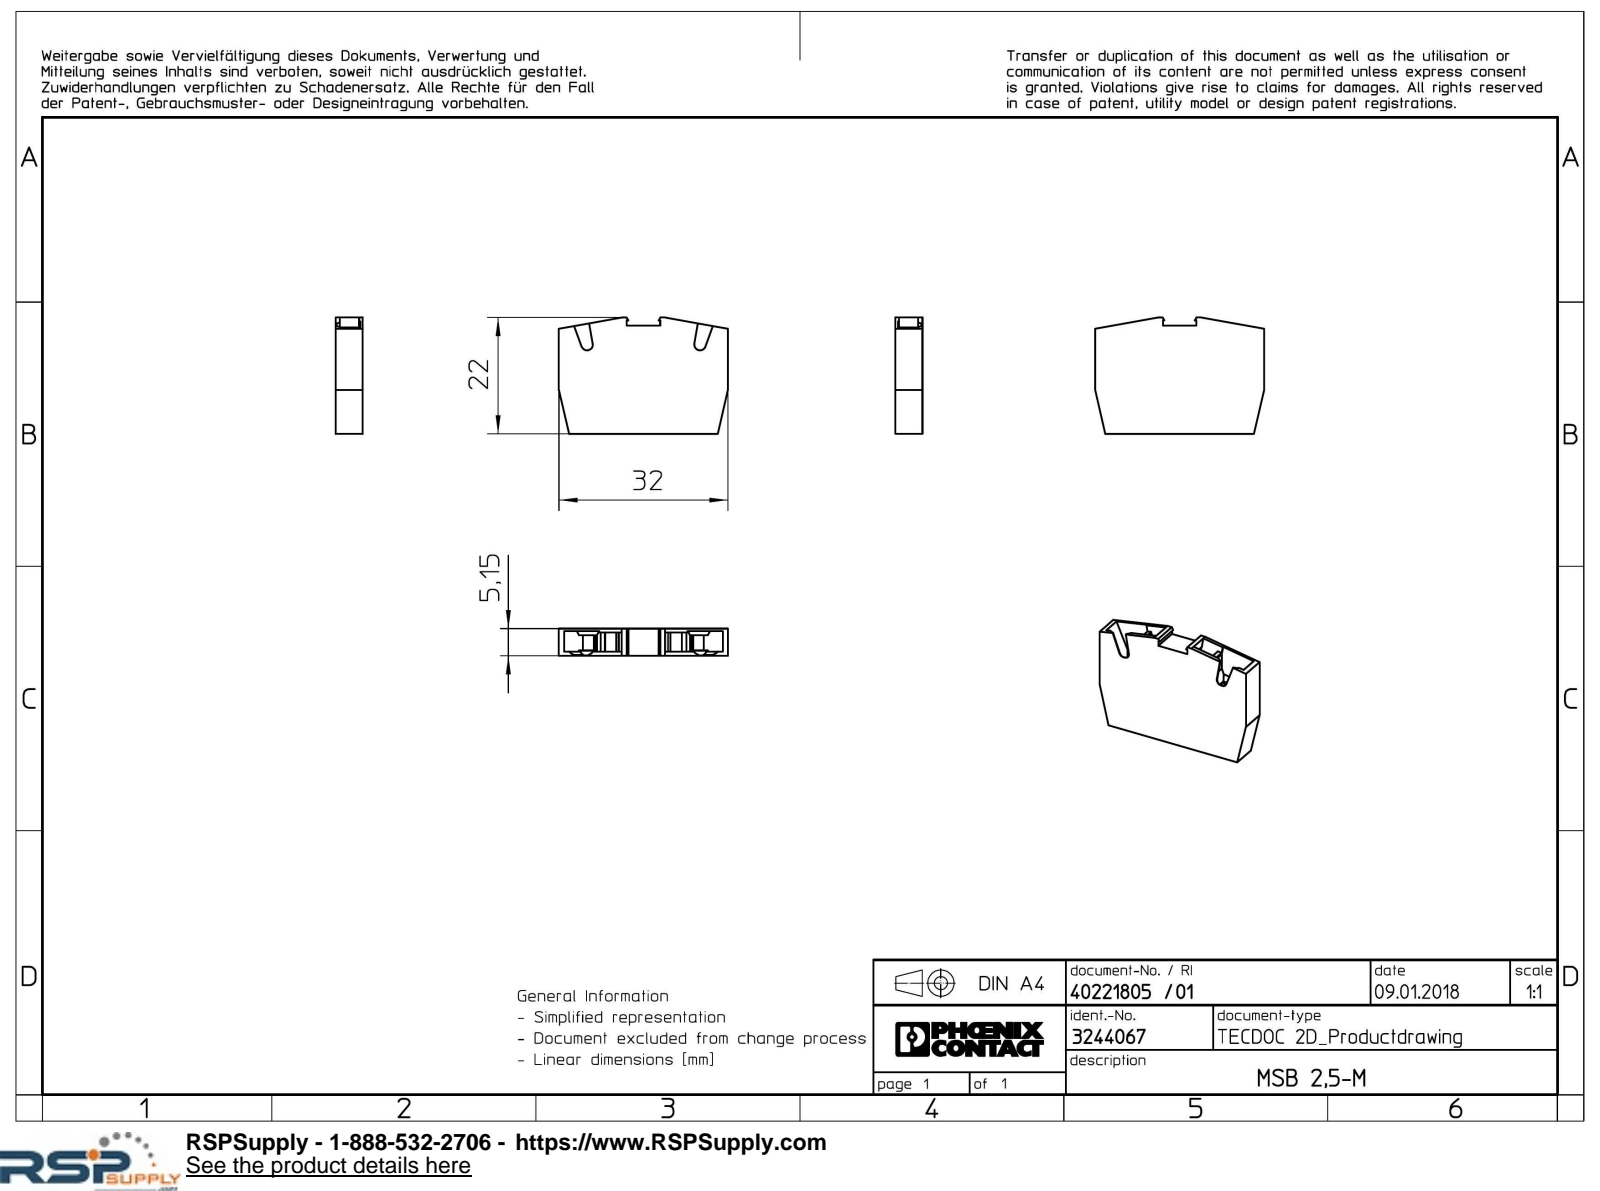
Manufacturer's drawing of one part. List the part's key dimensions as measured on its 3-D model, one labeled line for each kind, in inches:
Part name (STEP PRODUCT): MSB_2.5-M-select
STEP written by: Creo Elements/Direct Modeling 20.1A 29-Sep-2018 (C) Parametric Technology GmbH (AUTOMOTIVE_DESIGN)
Units: inches
Bodies: 1 solid, 92 faces (80 planar, 12 cylindrical, 0 other)
Overall size (bounding box): 1.26 × 0.866 × 0.203
Volume: 0.16 in³ · Surface area: 3.951 in²
Partial cylindrical surfaces — rounded edges, fillets, slot ends (radius × count): R0.039 ×4, R0.047 ×4, R0.094 ×2, R0.103 ×2
Main face-to-face distances: 0.203, 0.144, 0.171, 0.031, 0.028, 0.175, 0.02, 0.152, 0.183, 1.26
